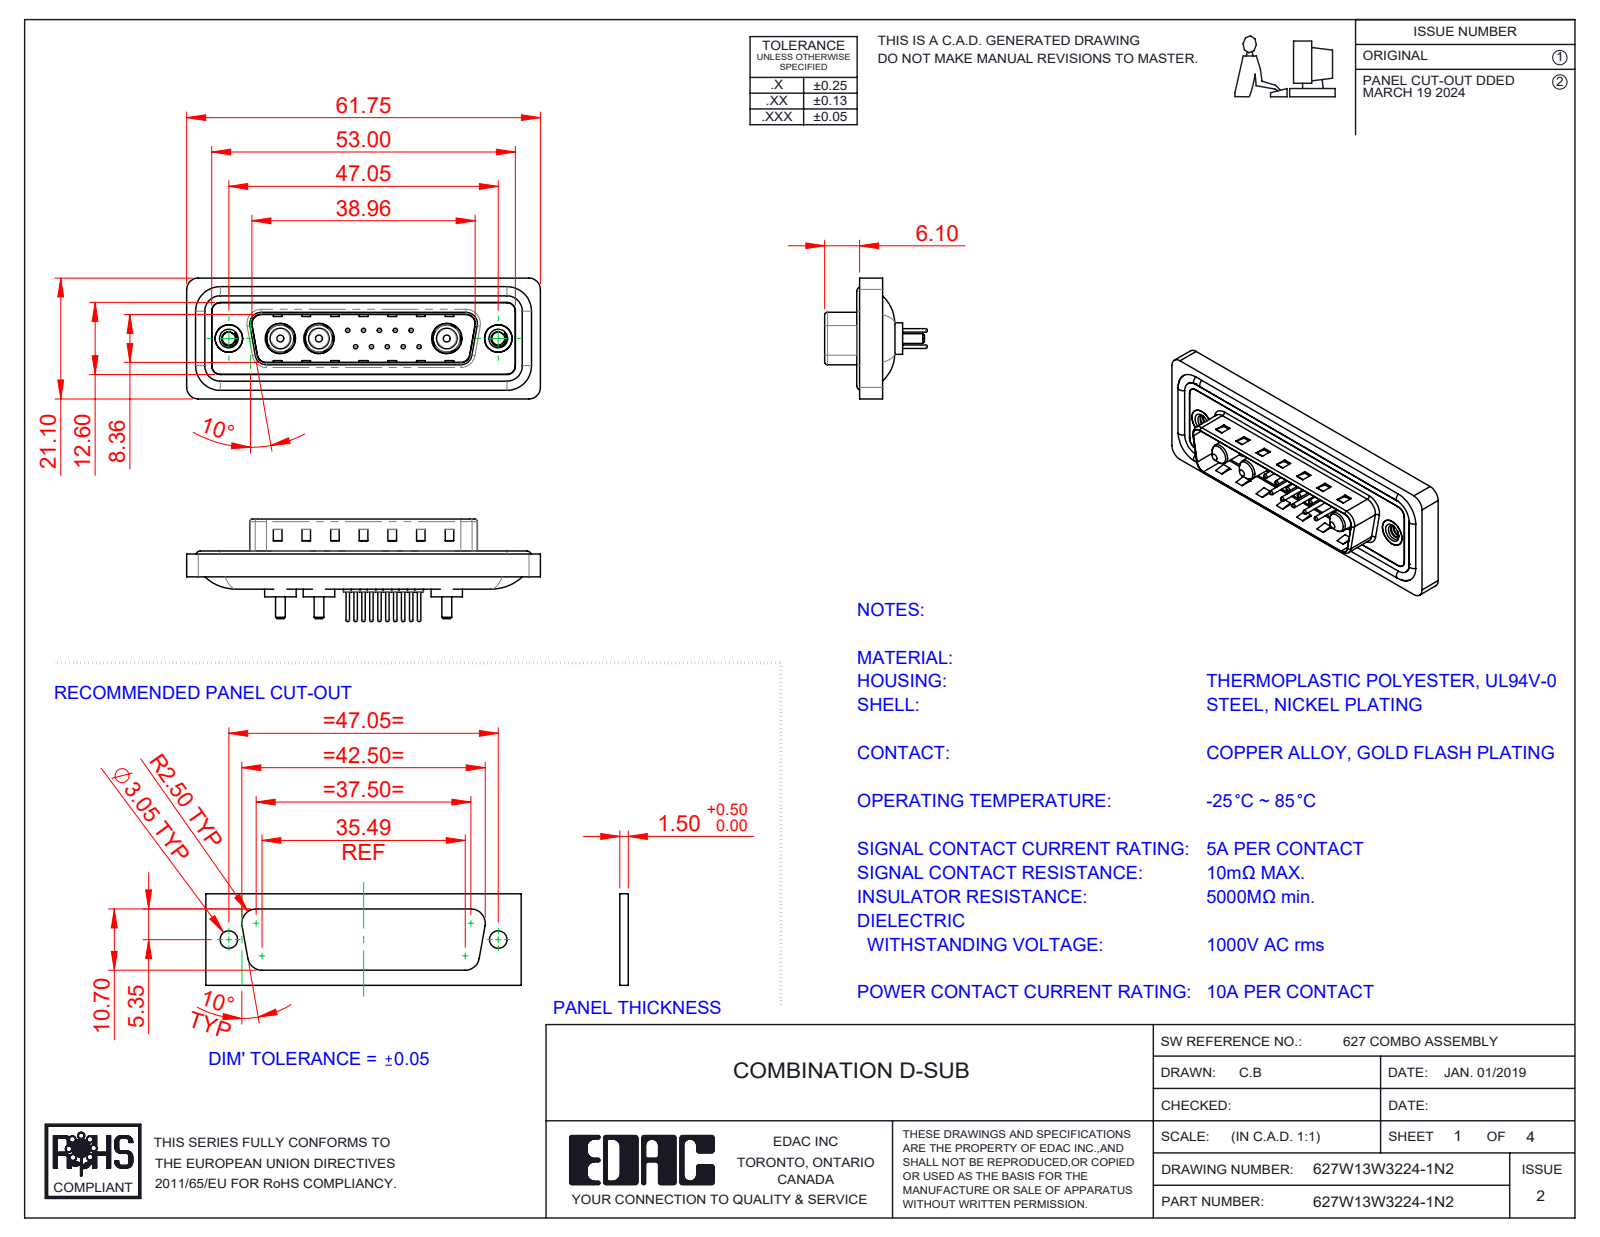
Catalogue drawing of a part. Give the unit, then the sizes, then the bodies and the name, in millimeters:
Units: millimetres
Overall size (bounding box): 61.75 × 21.1 × 17.9
Round holes (diameter × count): ⌀0.75 ×10, ⌀1.6 ×10, ⌀2 ×10, ⌀4.85 ×3, ⌀5.3 ×3, ⌀2.26 ×2, ⌀4 ×2, ⌀4.8 ×2, ⌀5 ×2
Round bosses / shafts (diameter × count): ⌀1.5 ×10, ⌀0.6 ×10, ⌀1.6 ×4, ⌀5.5 ×3, ⌀5.2 ×3, ⌀4.75 ×3, ⌀3.75 ×3, ⌀3.6 ×3
Partial cylindrical surfaces — rounded edges, fillets, slot ends (radius × count): R1.5 ×22, R2 ×18, R0.5 ×8, R1.6 ×8, R0.25 ×4, R0.6 ×4, R0.65 ×4, R0.9 ×4
Main face-to-face distances: 0.4, 1.5, 1.1, 1.6, 0.5, 3.1, 2.9, 0.82, 9.58, 4.1
Hole centre spacings: 3.16, 2.77, 5.04, 5.54, 7.49, 5.03, 8.31, 10.11
Volume: 7 291 mm³ · Surface area: 11 837 mm²
Bodies: 23 solids, 970 faces (309 planar, 385 cylindrical, 276 other)
Part name (STEP PRODUCT): Power Pin_10A S; 627Combo Waterproof Housing_25 Contacts; 627Combo Threaded Rivet_2; 627Combo Contact Row 2_24 (+5 more)
STEP written by: SolidWorks 2023 (CONFIG_CONTROL_DESIGN)
